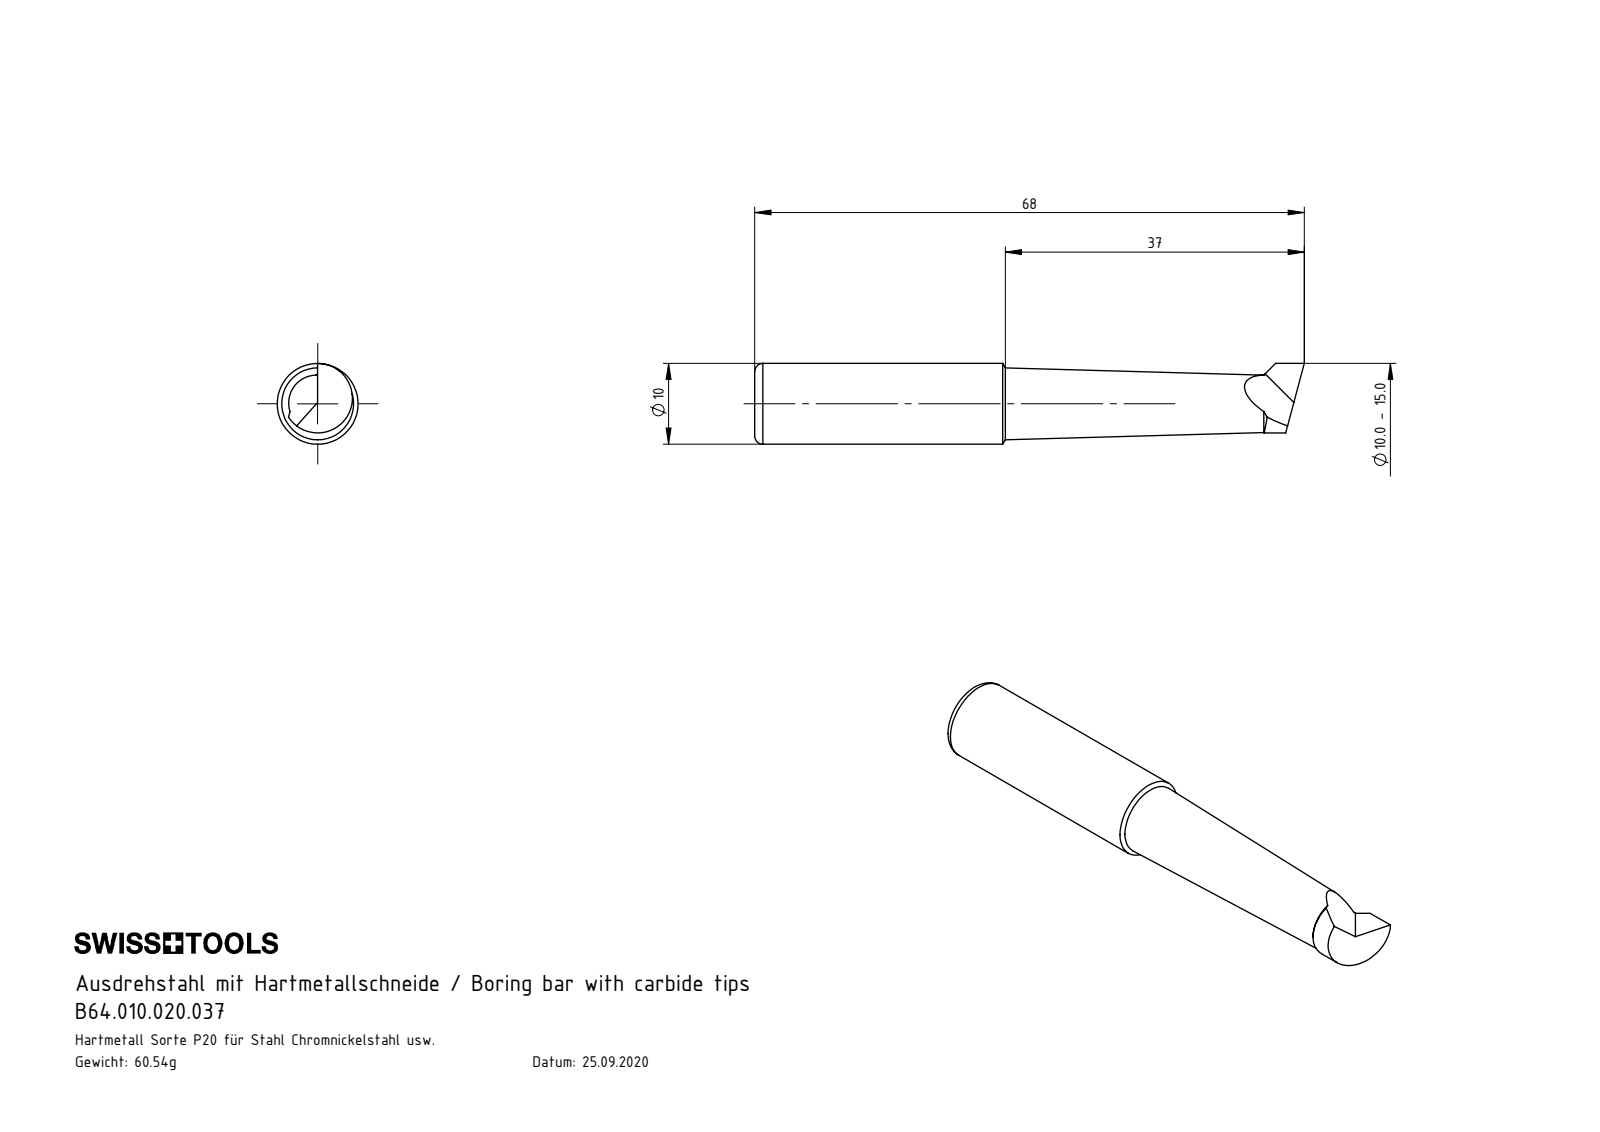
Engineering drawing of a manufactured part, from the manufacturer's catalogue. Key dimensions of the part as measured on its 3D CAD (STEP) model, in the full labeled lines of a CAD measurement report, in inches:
Part name (STEP PRODUCT): B64.010.020.037
STEP written by: SolidWorks 2022 (CONFIG_CONTROL_DESIGN)
Units: inches
Bodies: 1 solid, 16 faces (4 planar, 3 cylindrical, 9 other)
Overall size (bounding box): 2.677 × 0.394 × 0.394
Volume: 0.255 in³ · Surface area: 3.08 in²
Round bosses / shafts (diameter × count): ⌀0.394 ×1
Partial cylindrical surfaces — rounded edges, fillets, slot ends (radius × count): R0.169 ×1
